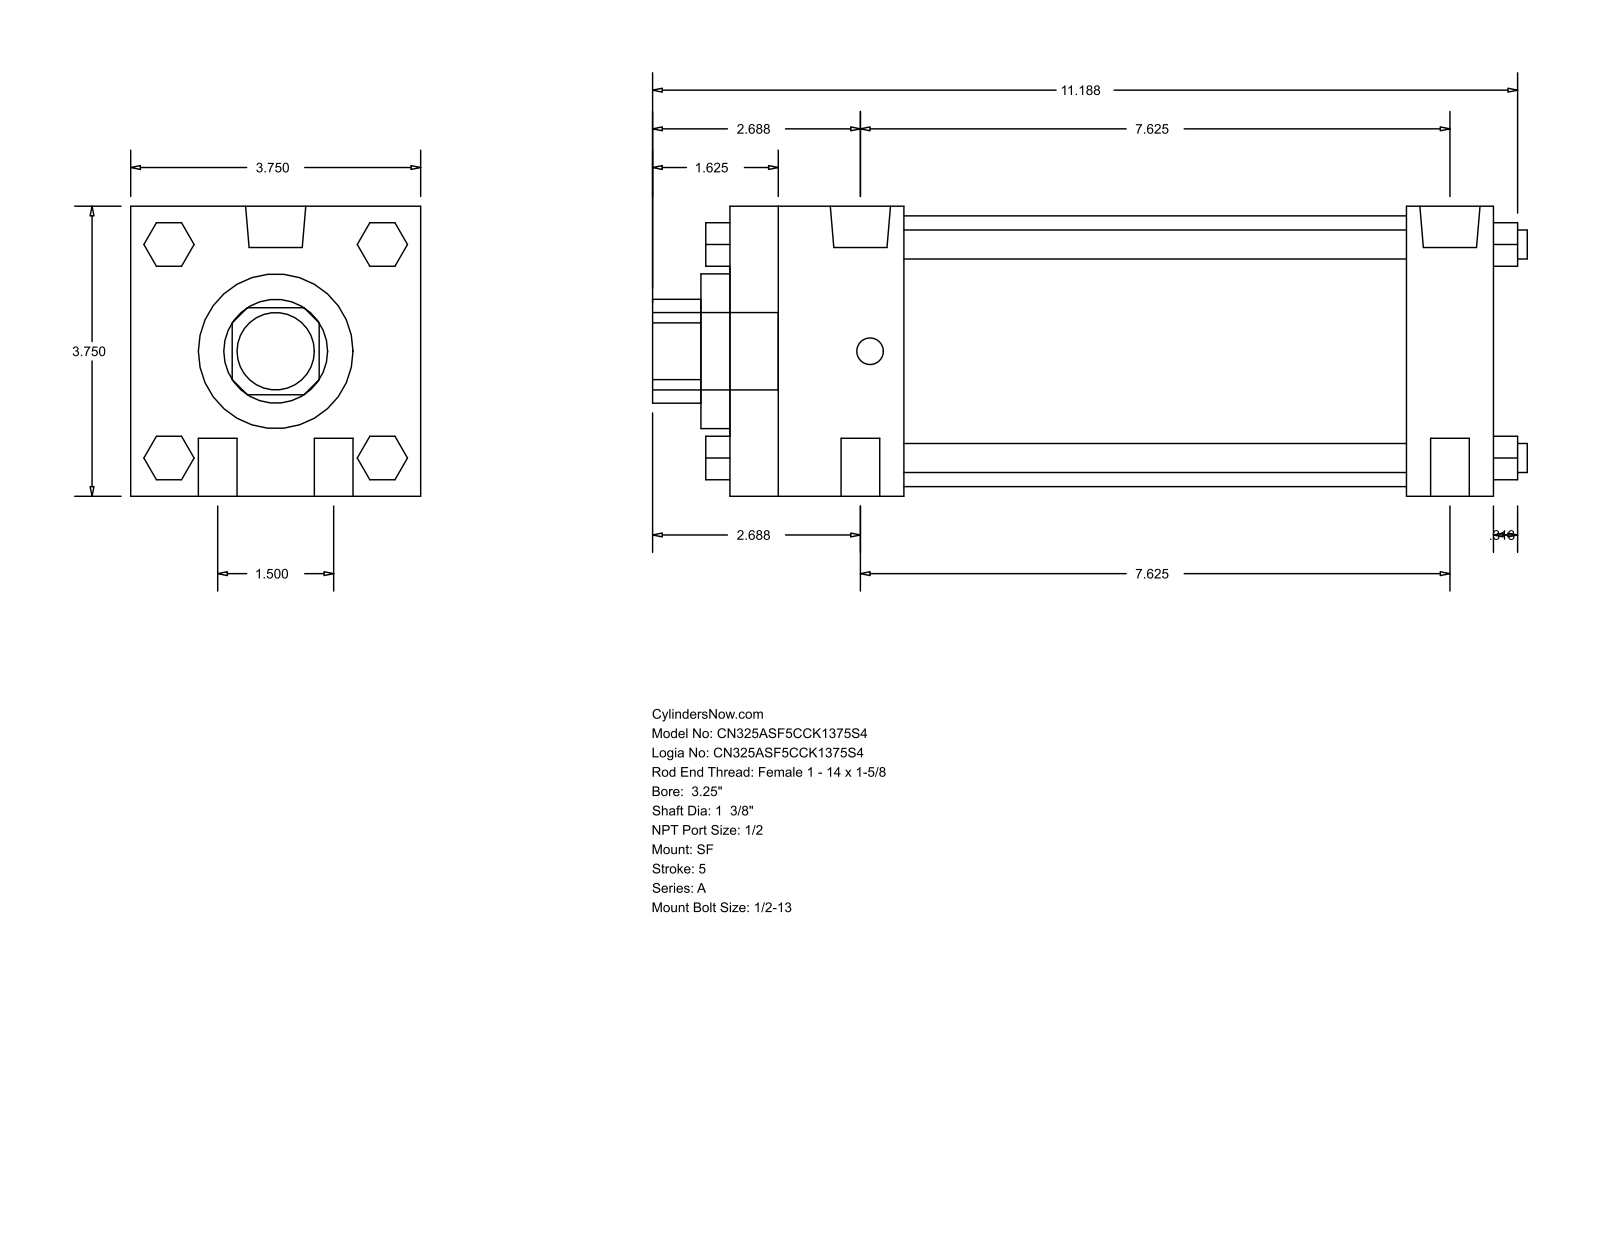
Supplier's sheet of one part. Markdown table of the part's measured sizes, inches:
| quantity | value |
| --- | --- |
| part name | A_SF__0325_1.375 |
| STEP written by | GSSL Pune (CONFIG_CONTROL_DESIGN) |
| units | inches |
| bodies | 0 solids, 124 faces (94 planar, 30 cylindrical, 0 other) |
| overall size | 11.313 × 3.75 × 3.75 |
| round holes (diameter × count) | 1.375 × 1, 2 × 1, 3.5 × 1 |
| round bosses / shafts (diameter × count) | 0.5 × 4, 0.375 × 4, 0.778 × 2, 0.344 × 2, 1 × 1 |
| partial cylindrical surfaces (radius × count) | 0.672 × 1 |
| main face-to-face distances | 3.75, 9.875, 1.125, 8.75, 2.25, 6.5, 7.625, 0.375, 2.625, 9.125 |
